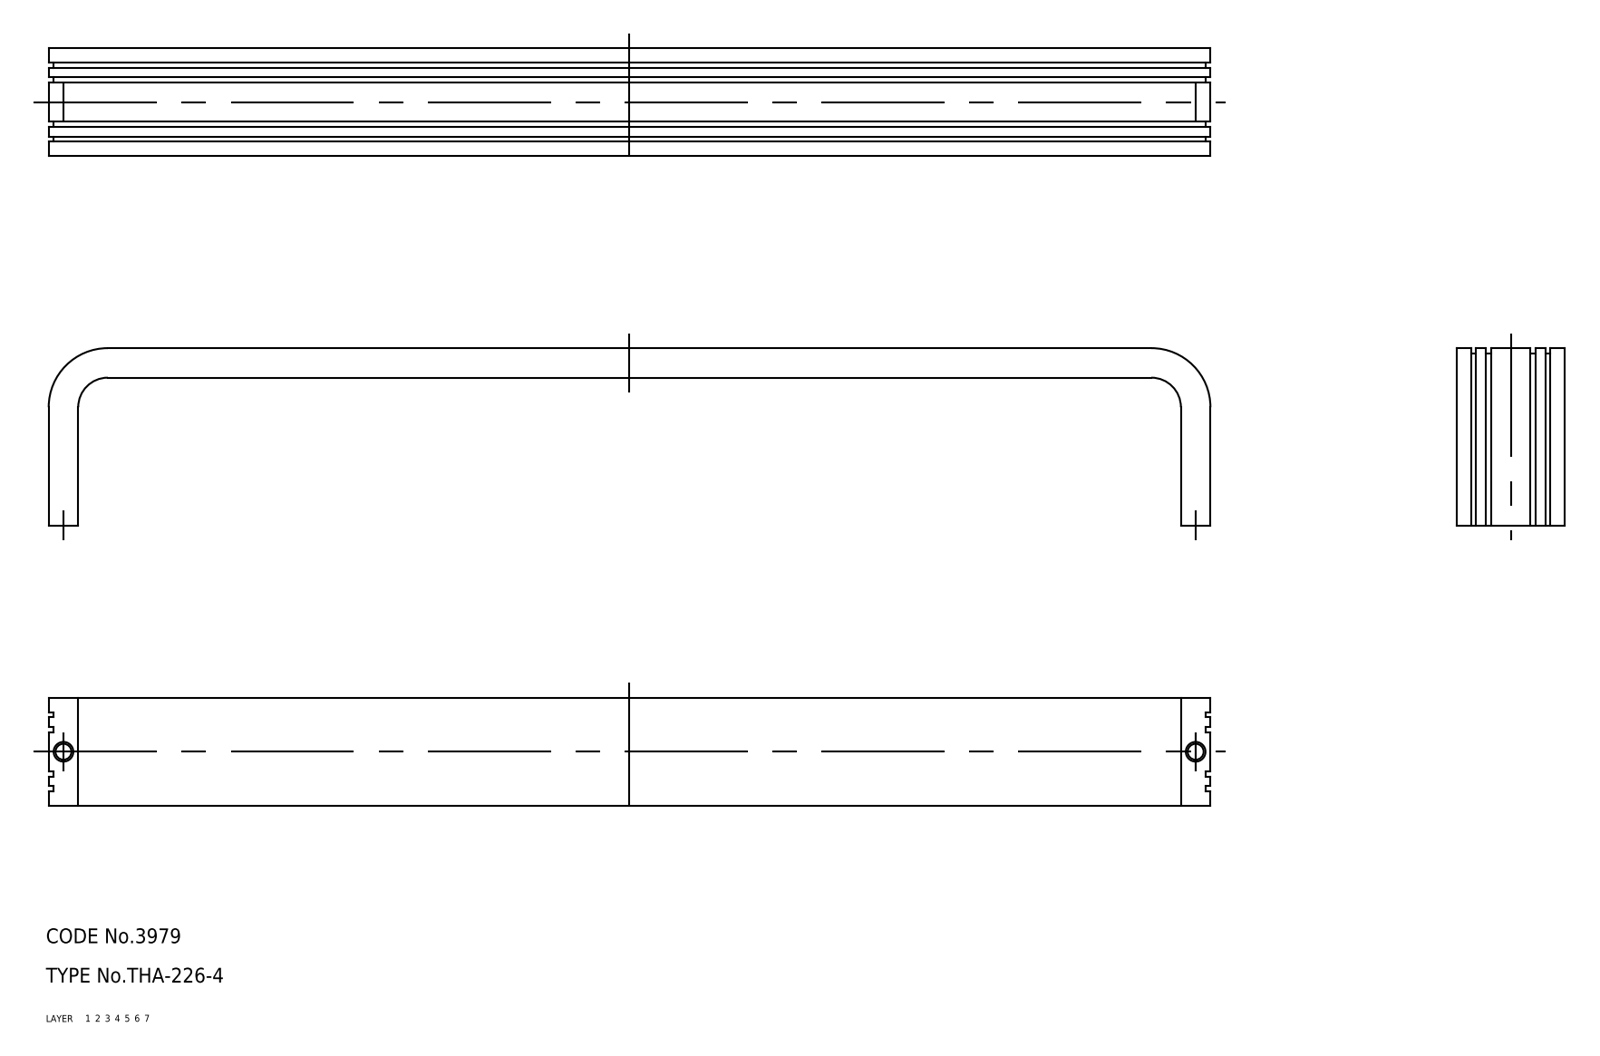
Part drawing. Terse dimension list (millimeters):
name: pull
written by: CADfix (AUTOMOTIVE_DESIGN)
unit: mm
bodies: 1 solid, 68 faces (0 planar, 0 cylindrical, 68 other)
size: 236 × 36 × 22
volume: 36 717 mm³; area: 18 907 mm²
